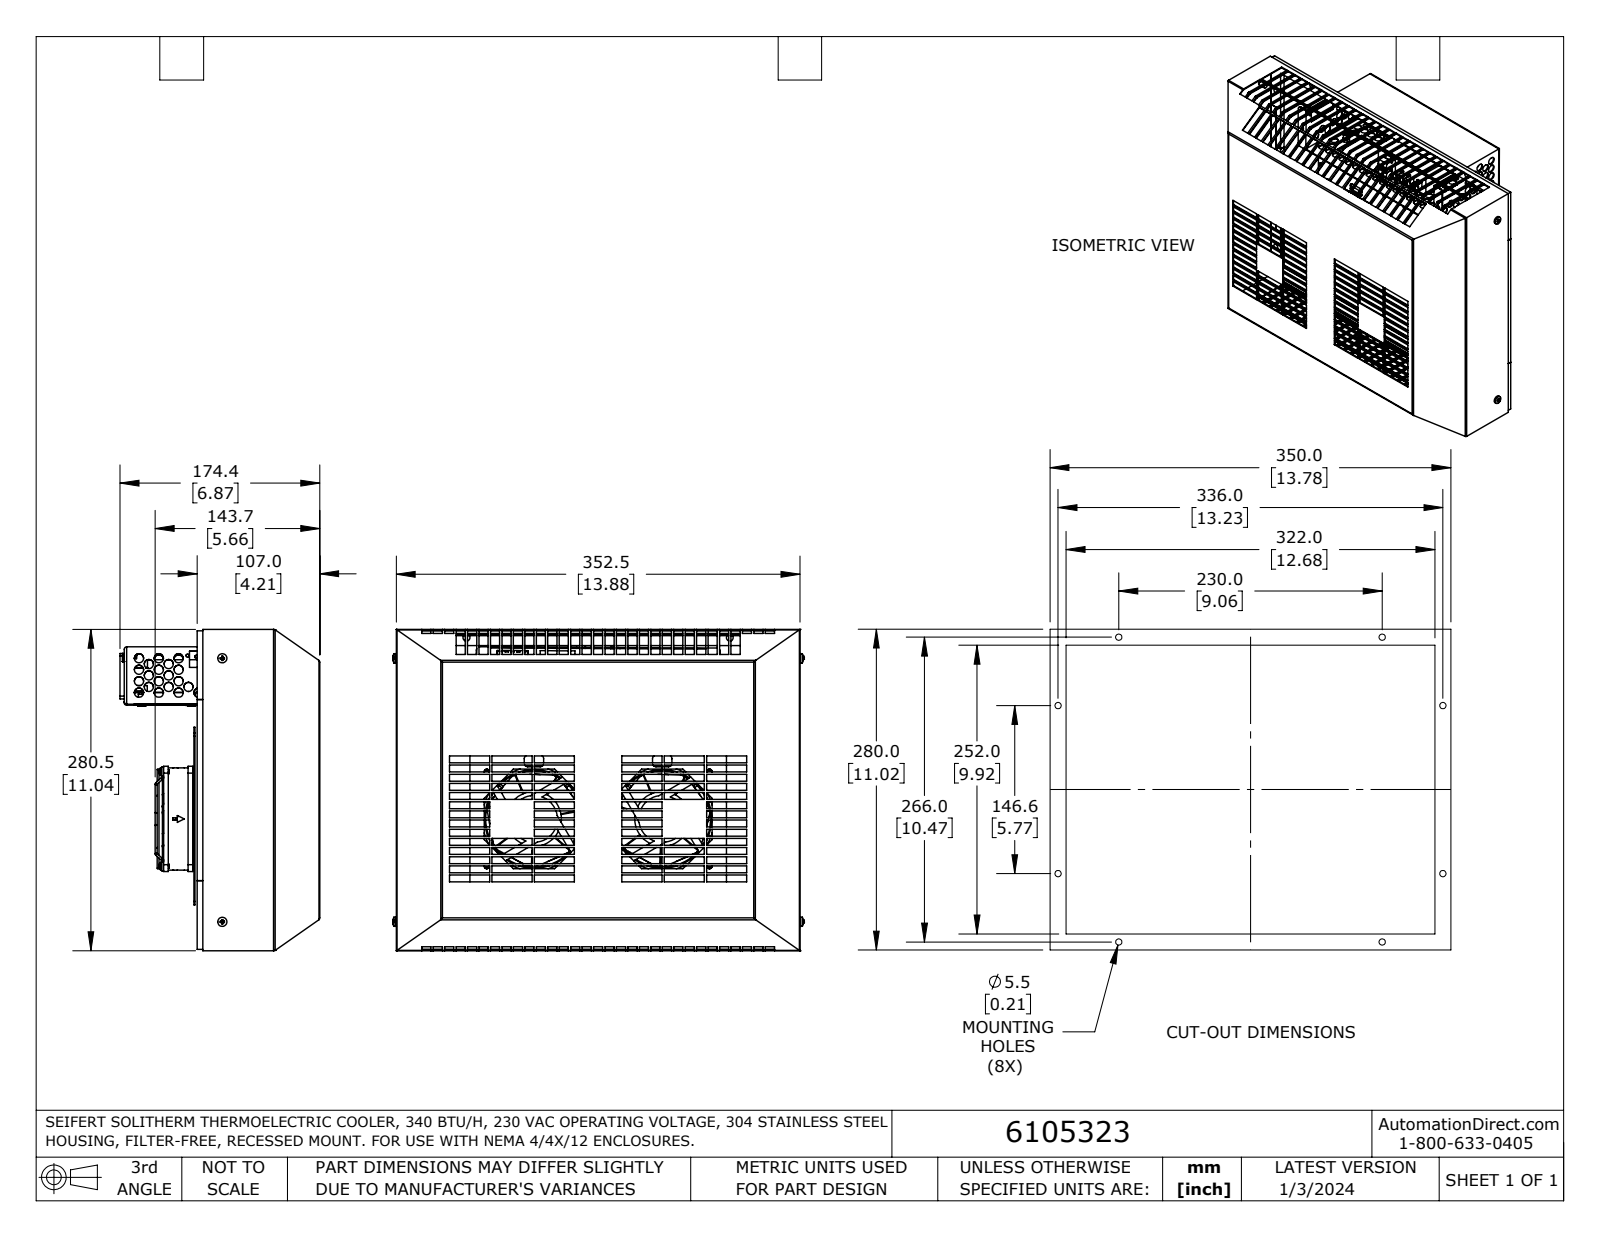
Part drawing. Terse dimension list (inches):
name: 61053013
written by: SolidWorks 2023 (AUTOMOTIVE_DESIGN)
unit: in
bodies: 38 solids, 3447 faces (2488 planar, 579 cylindrical, 380 other)
size: 14.118 × 11.043 × 6.866
volume: 38.3 in³; area: 957.9 in²
holes: 125× ⌀0.315, 10× ⌀0.177, 9× ⌀0.154, 8× ⌀0.169, 8× ⌀0.236, 6× ⌀0.138, 4× ⌀0.098, 4× ⌀0.106, 4× ⌀0.142, 2× ⌀0.059, 2× ⌀0.067, 2× ⌀0.096
bosses: 24× ⌀0.071, 9× ⌀0.15, 8× ⌀0.154, 8× ⌀0.094, 4× ⌀0.276, 4× ⌀0.236, 2× ⌀3.515, 2× ⌀1.887
rounds: 27× R0.039, 18× R0.01, 18× R0.118, 16× R0.006, 16× R0.079, 9× R0.114, 8× R0.236, 4× R0.02
face distances: 0.039, 4.287, 13.839, 4.326, 0.197, 0.311, 4.248, 2.39, 6.677, 3.976
hole spacings: 0.394, 0.395, 0.787, 0.787, 1.041, 0.392, 0.681, 0.683
